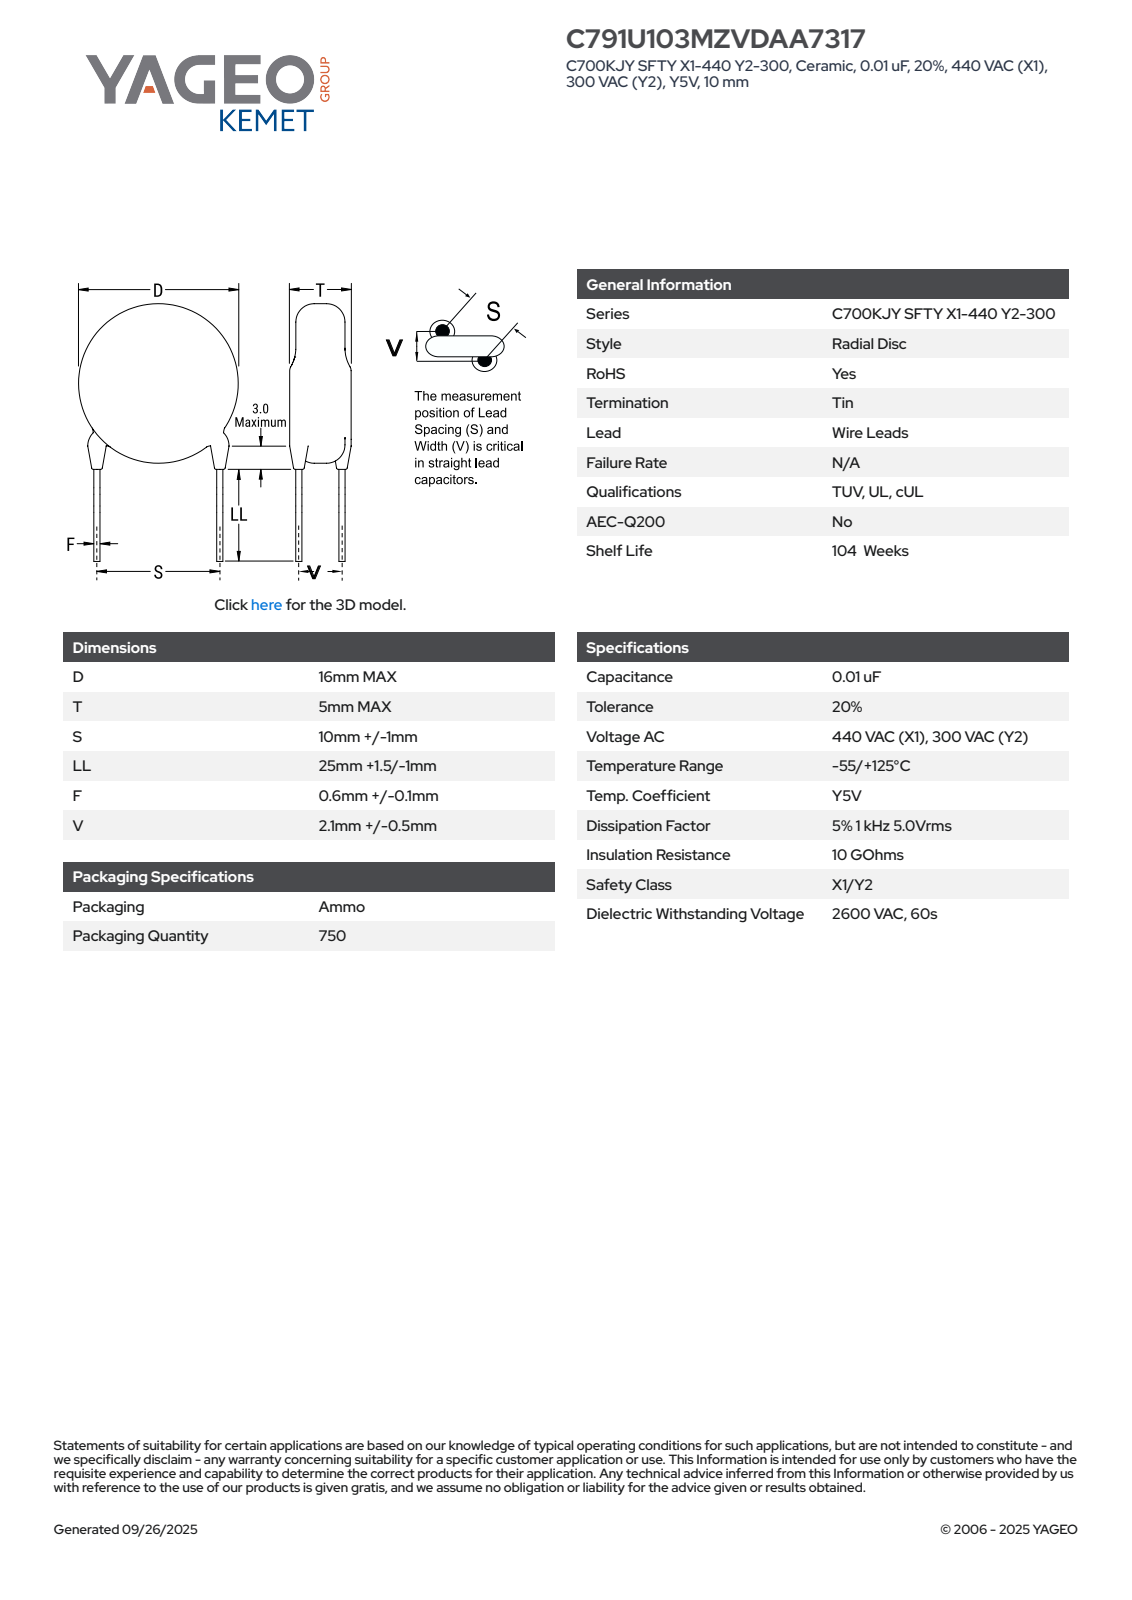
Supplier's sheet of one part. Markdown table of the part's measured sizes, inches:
| quantity | value |
| --- | --- |
| part name | CCD_KST_16X5_D16T5S10.1LL26.5F0.7V2.1 |
| STEP written by | SolidWorks 2021 (AUTOMOTIVE_DESIGN) |
| units | inches |
| bodies | 4 solids, 77 faces (63 planar, 10 cylindrical, 4 other) |
| overall size | 1.673 × 0.63 × 0.197 |
| volume | 0.062 in³ |
| surface area | 1.18 in² |
| round bosses / shafts (diameter × count) | 0.047 × 2, 0.028 × 2, 0.63 × 1 |
| main face-to-face distances | 0.197, 1.043, 1.413, 0.37, 1.341, 0.297, 0.072, 0.02, 0.014, 0.059 |
